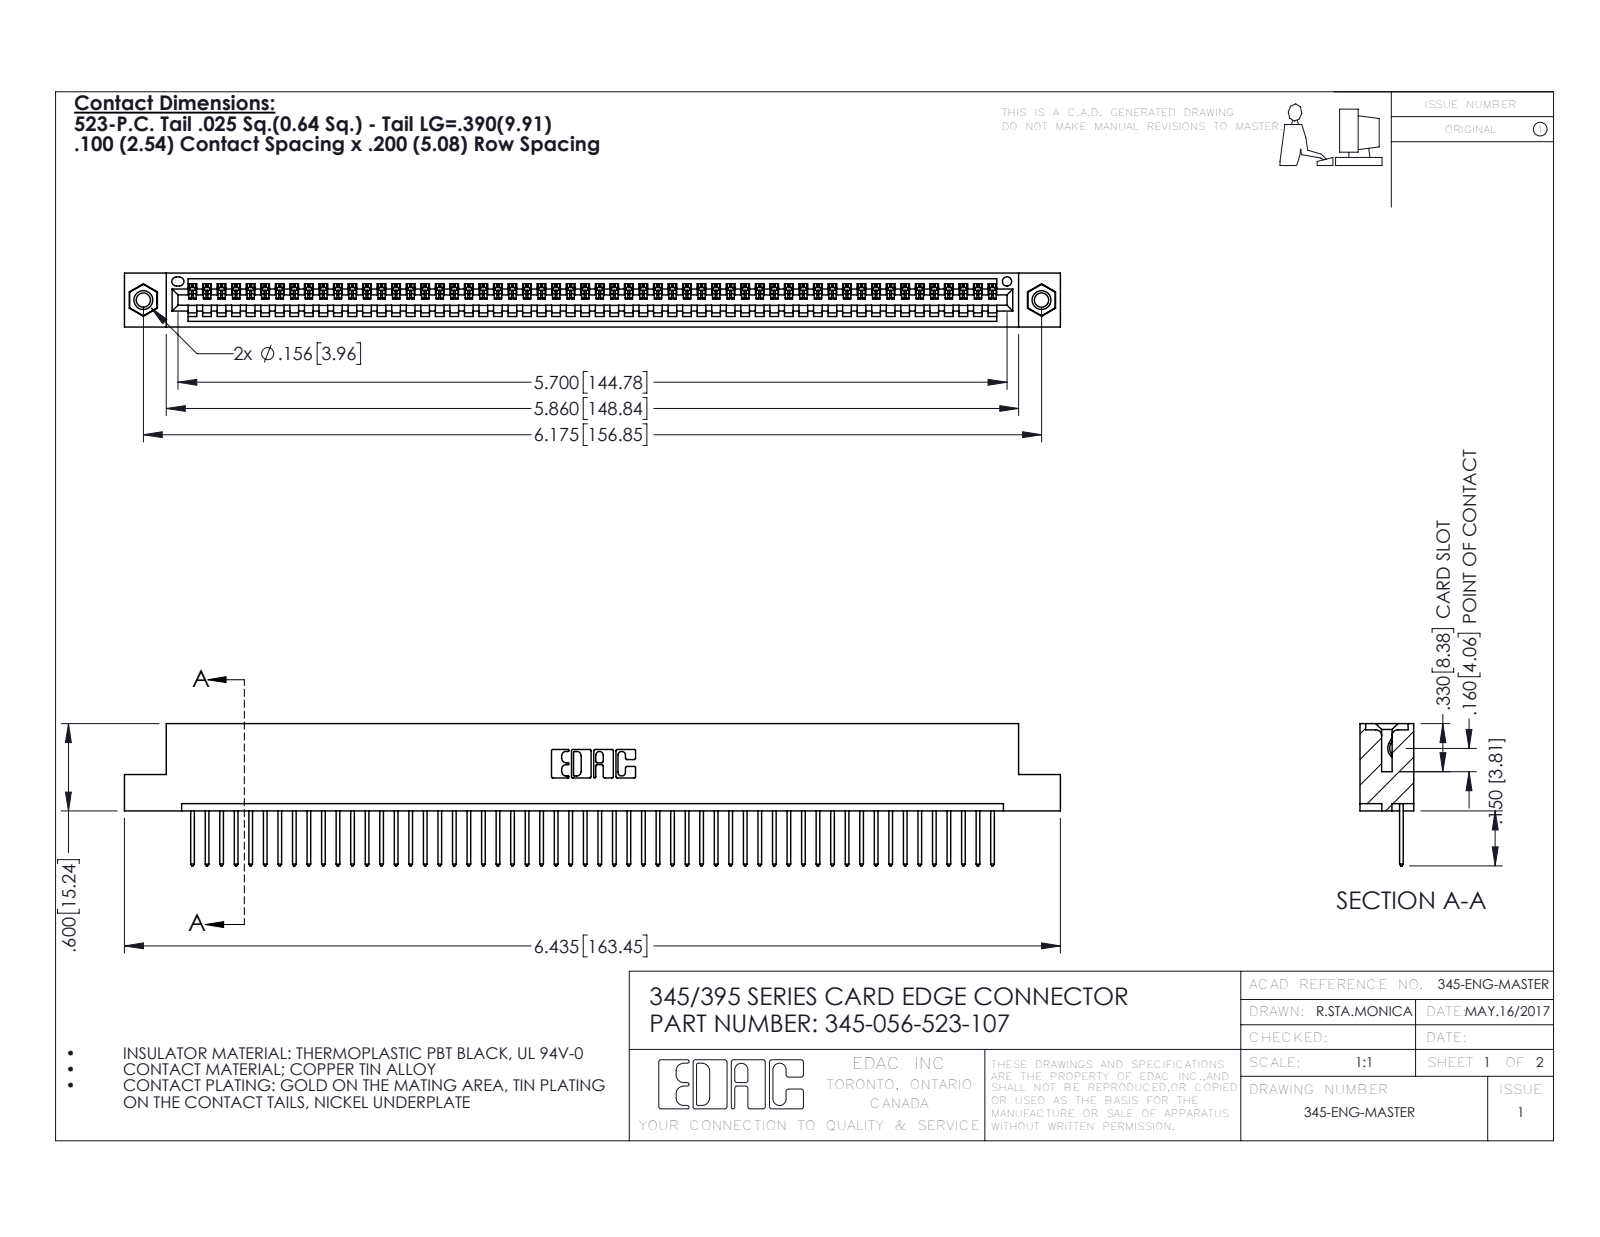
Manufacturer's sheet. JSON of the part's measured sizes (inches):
{"part_name": "345-250-001_345-250-005-103; 345 Part_Flush Mounting Lugs - 0.156 Dia-TI; 345-056-523-107; 345-292-001_345-293-123", "step_written_by": "SolidWorks 2016 (CONFIG_CONTROL_DESIGN)", "units": "inches", "bodies": {"solids": 59, "faces": 3434, "planar": 2352, "cylindrical": 1066, "other": 16}, "overall_size": [6.435, 0.977, 0.37], "volume_in3": 0.952, "surface_area_in2": 32.58, "round_holes": [[0.098, 2], [0.125, 2], [0.156, 2], [0.064, 1]], "round_bosses_or_shafts": [[0.155, 2]], "partial_cylinders_radius": [[0.006, 112], [0.01, 112], [0.01, 22], [0.007, 6], [0.031, 6], [0.026, 3], [0.031, 2], [0.04, 2]], "face_to_face_distances": [0.072, 0.298, 0.37, 0.2, 0.098, 0.272, 0.025, 0.225, 0.149, 0.072], "hole_center_spacings": [0.27, 5.939, 6.175]}
